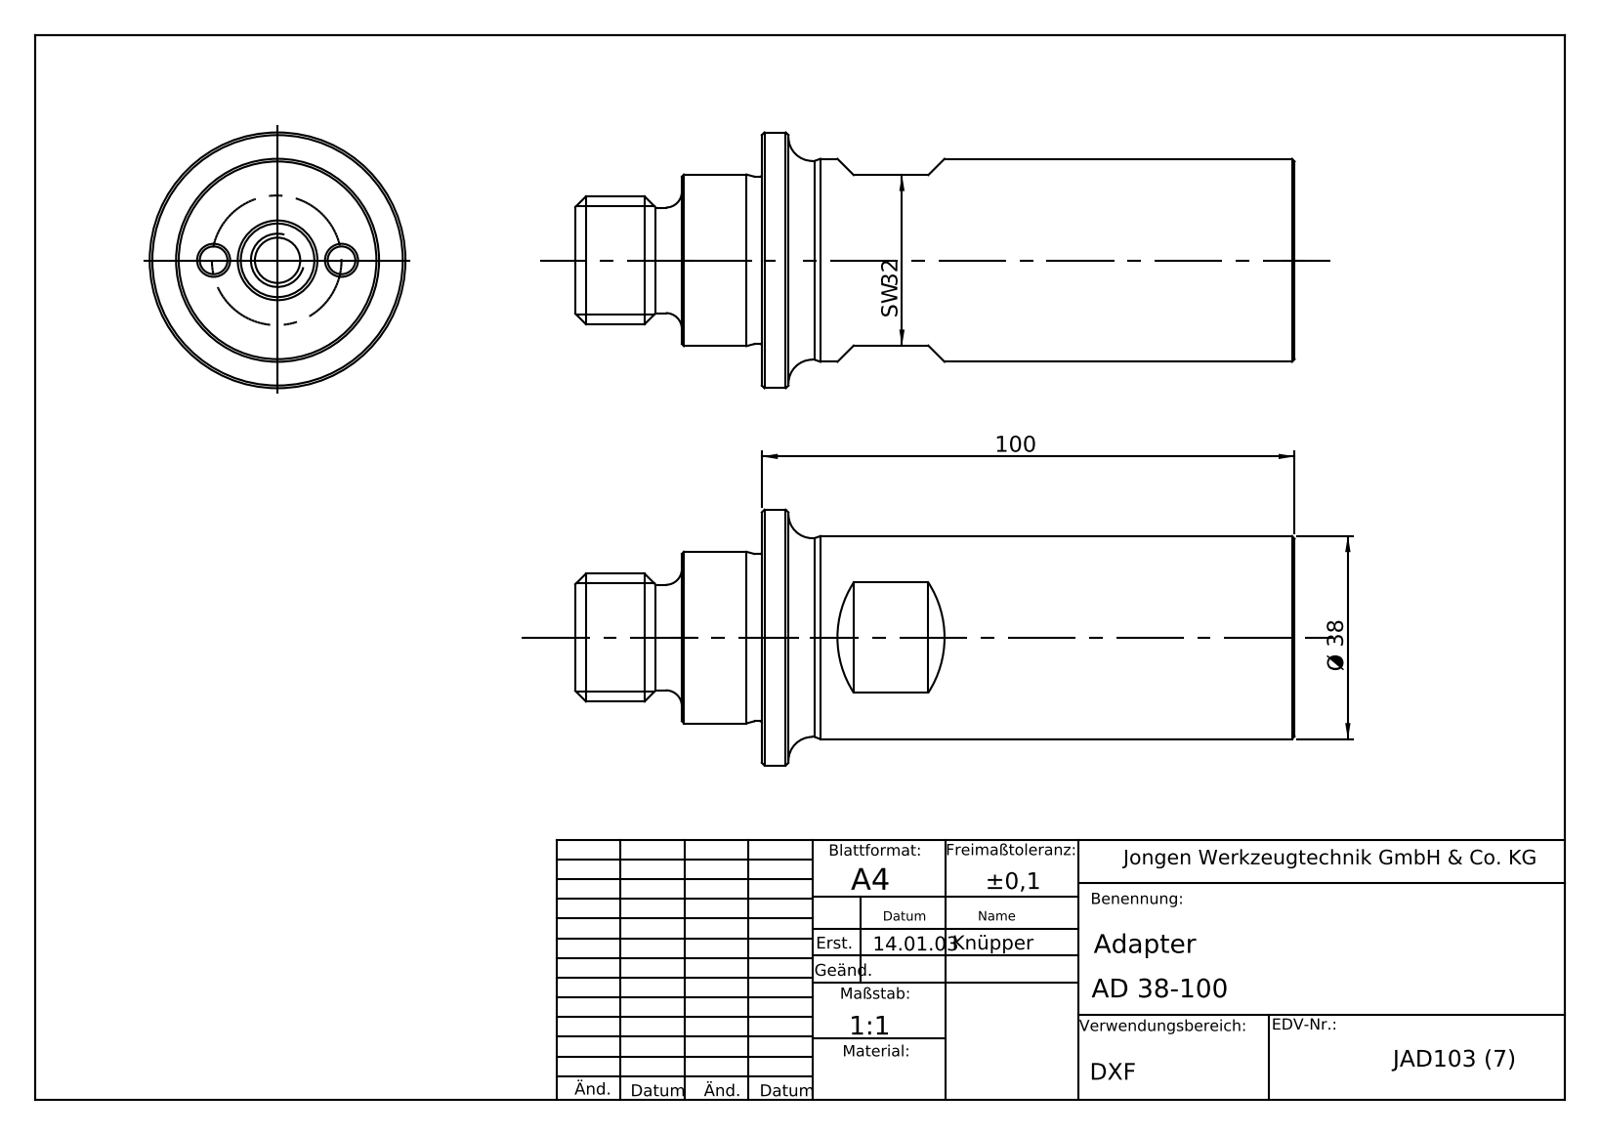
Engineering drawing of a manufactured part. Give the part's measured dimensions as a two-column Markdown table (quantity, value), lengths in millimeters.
| quantity | value |
| --- | --- |
| part name | AD 38-100 |
| STEP written by | SolidWorks 2012 (AUTOMOTIVE_DESIGN) |
| units | millimeters |
| bodies | 1 solid, 83 faces (11 planar, 26 cylindrical, 46 other) |
| overall size | 135 × 48 × 48 |
| volume | 132 483 mm³ |
| surface area | 20 083 mm² |
| round holes (diameter × count) | 5.2 × 2, 3.15 × 1, 8.5 × 1, 13.8 × 1, 14.2 × 1 |
| round bosses / shafts (diameter × count) | 48 × 1, 38.1 × 1, 37.3 × 1, 32.2 × 1, 31.4 × 1, 24 × 1, 19.8 × 1 |
| main face-to-face distances | 100, 20, 32, 35, 135, 15, 115, 12.73, 40, 5 |
| hole center spacings | 12, 24 |
